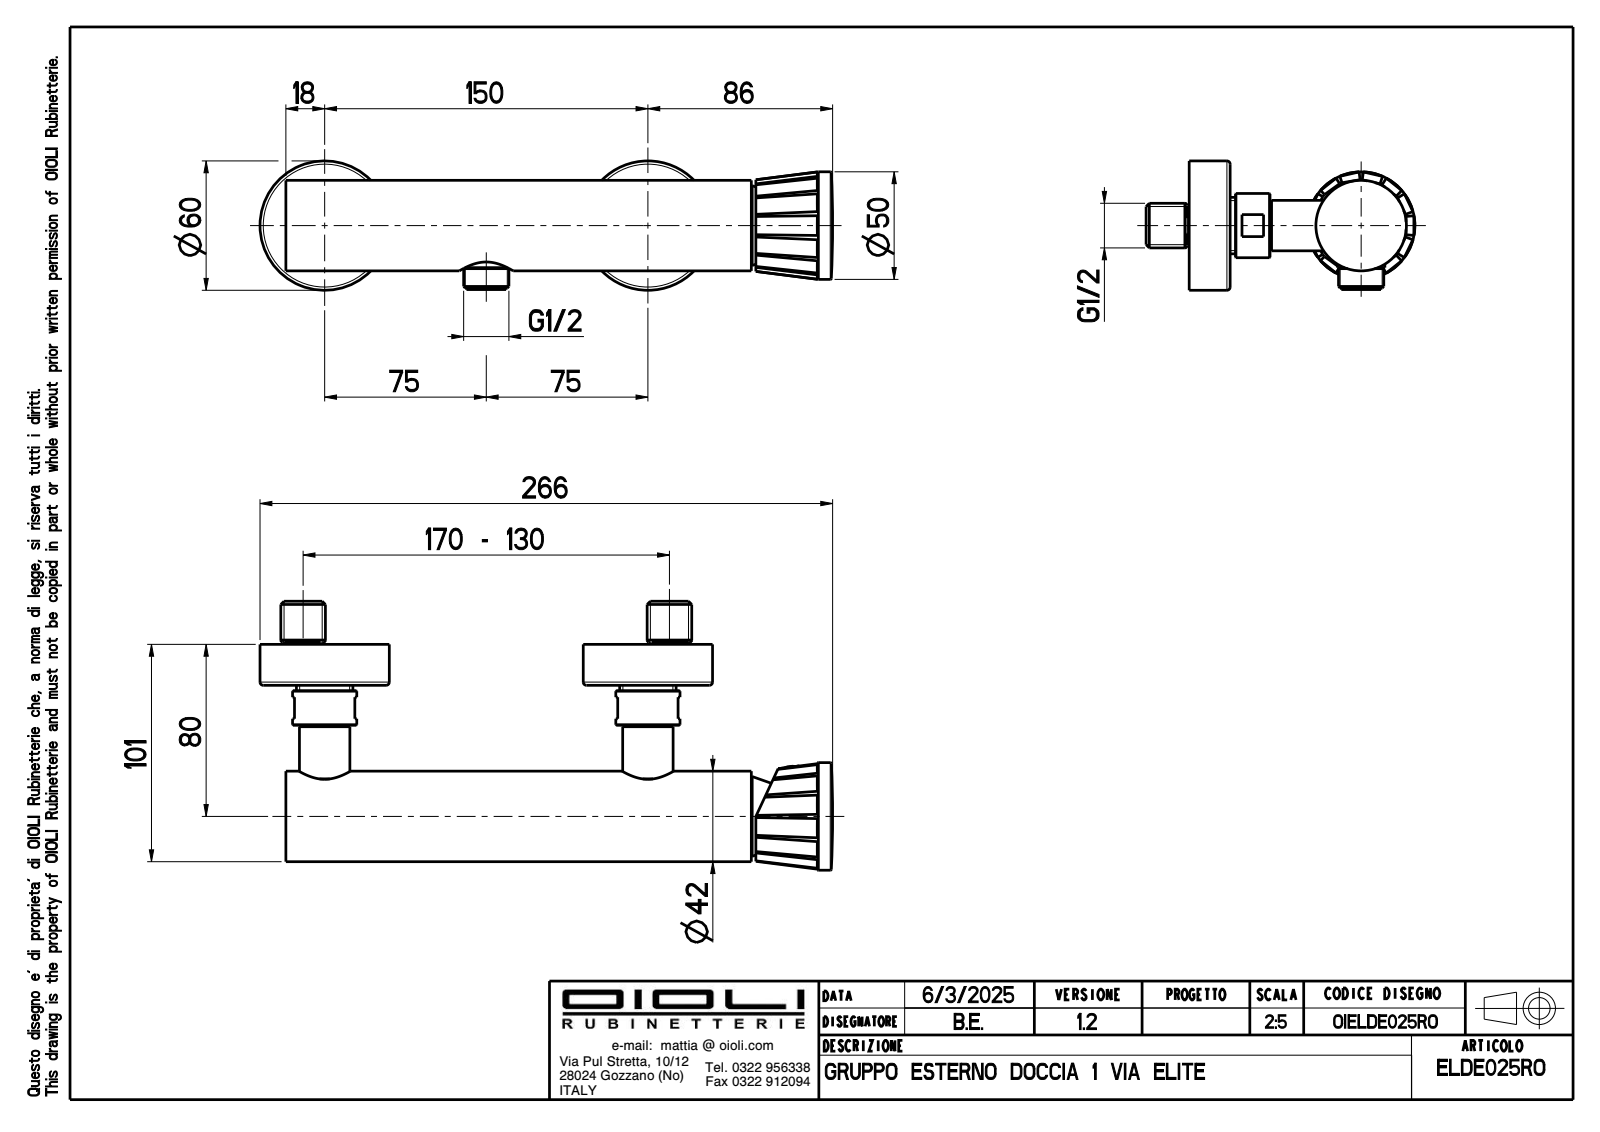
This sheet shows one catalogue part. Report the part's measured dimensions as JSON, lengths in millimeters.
{"part_name": "OIBR00271; OIAQ00285; OIBR00998; OIAQ00028 (+8 more)", "step_written_by": "CREO PARAMETRIC BY PTC INC, 2024493 (CONFIG_CONTROL_DESIGN)", "units": "millimeters", "bodies": {"solids": 15, "faces": 695, "planar": 208, "cylindrical": 246, "other": 241}, "overall_size": [265.72, 124.75, 60], "volume_mm3": 321963, "surface_area_mm2": 132562, "round_holes": [[4, 3], [7, 3], [10, 3], [5, 2], [8, 2], [10.5, 2], [15.5, 2], [16.7, 2], [19, 2], [19.1, 2], [20, 2], [21.8, 2]], "round_bosses_or_shafts": [[60, 2], [29.8, 2], [27.2, 2], [26.4, 2], [26.2, 2], [23.4, 2], [23.2, 2], [23, 2]], "partial_cylinders_radius": [[0.1, 10], [1, 8], [7.5, 4], [0.5, 2], [5.5, 1]], "face_to_face_distances": [0.7, 13, 250.6, 15.5, 19, 0.5, 5.5, 182.5, 68.1, 18.5], "hole_center_spacings": [6.28, 8.6, 10, 13.45, 15.13, 21.93, 160, 3]}
